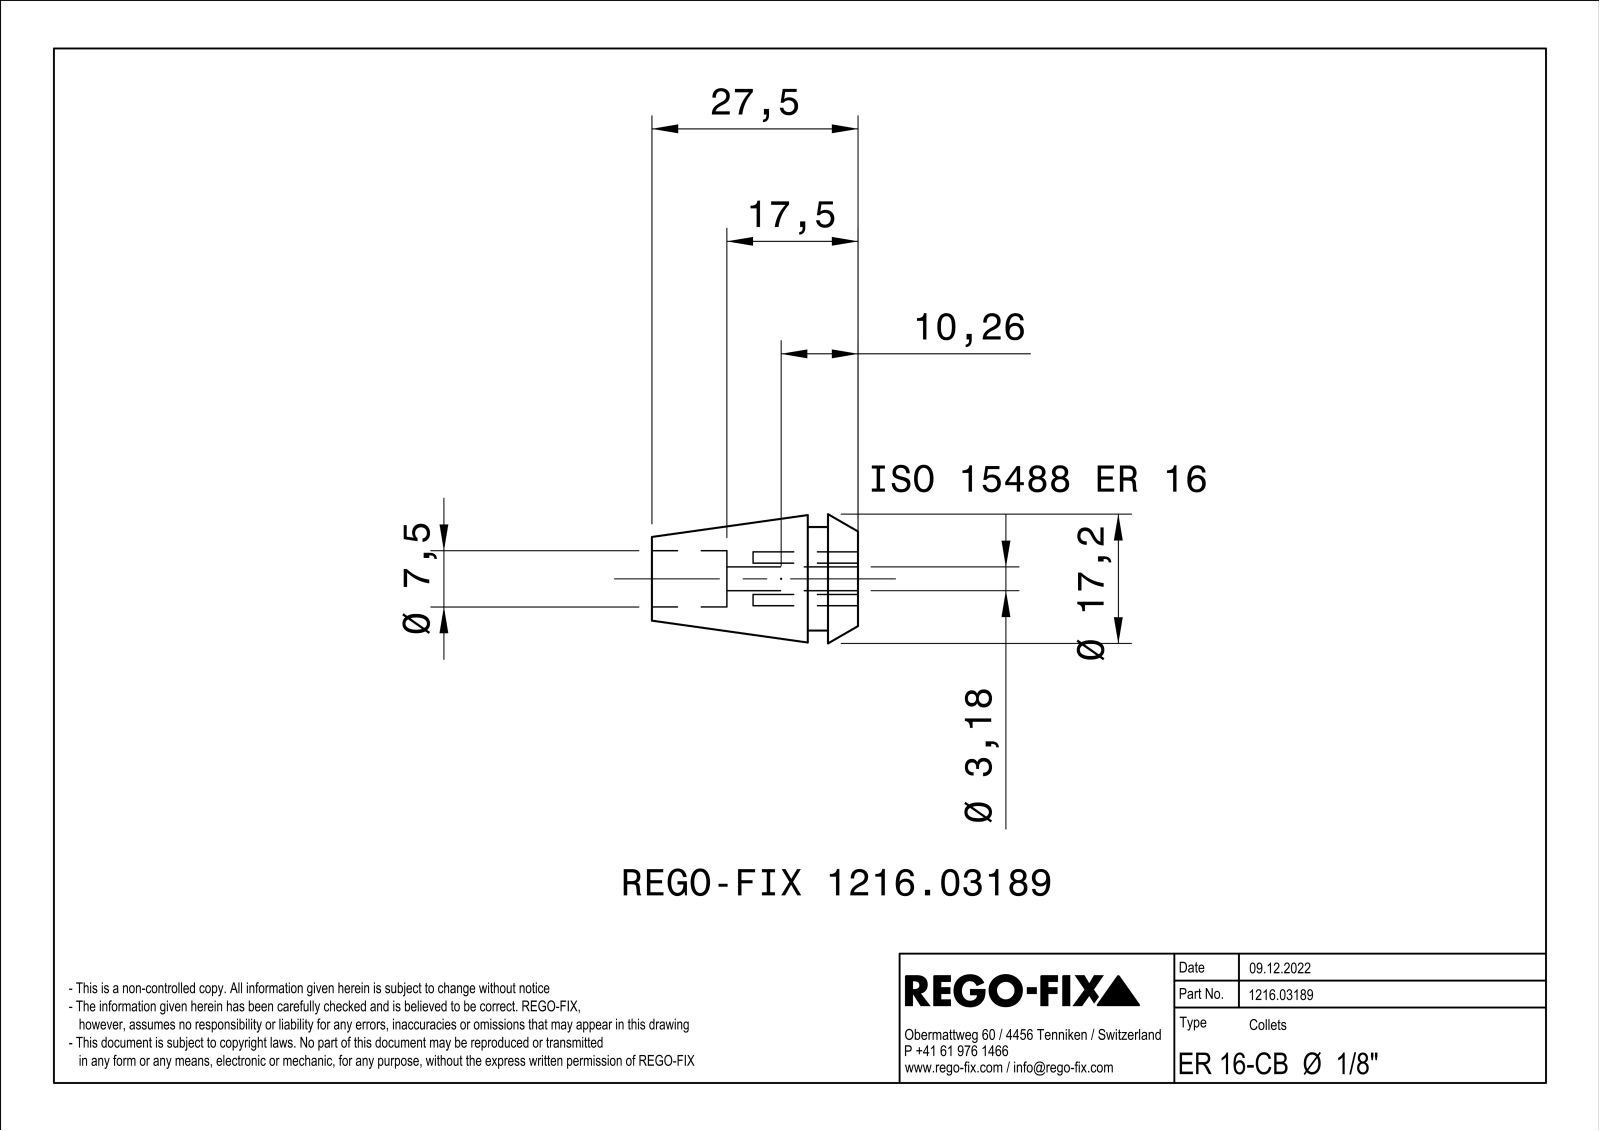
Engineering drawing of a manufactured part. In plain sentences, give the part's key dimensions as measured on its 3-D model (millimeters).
The part is named "NOCUT". Its 3-D file was written by "SIEMENS PLM Software Solid Edge ST10 (AUTOMOTIVE_DESIGN)". It is 1 solid with 118 faces: 36 planar, 17 cylindrical and 65 other. Overall it measures 27.5 by 16.9 by 16.9 millimeters. Its volume is 3 522 cubic millimeters and its surface area 3 500 square millimeters. Round holes: 4 of diameter 1.5, 1 of diameter 3.17, 1 of diameter 7.5. Round bosses or shafts: 1 of diameter 16.74, 1 of diameter 13.8. The main face-to-face distances are 0.5, 4, 6.7, 2.7, 27.5, 23.5, 20.8, 22.5, 18.5, 15.8. The hole center spacings are 2.84, 4.02, 5.69.
